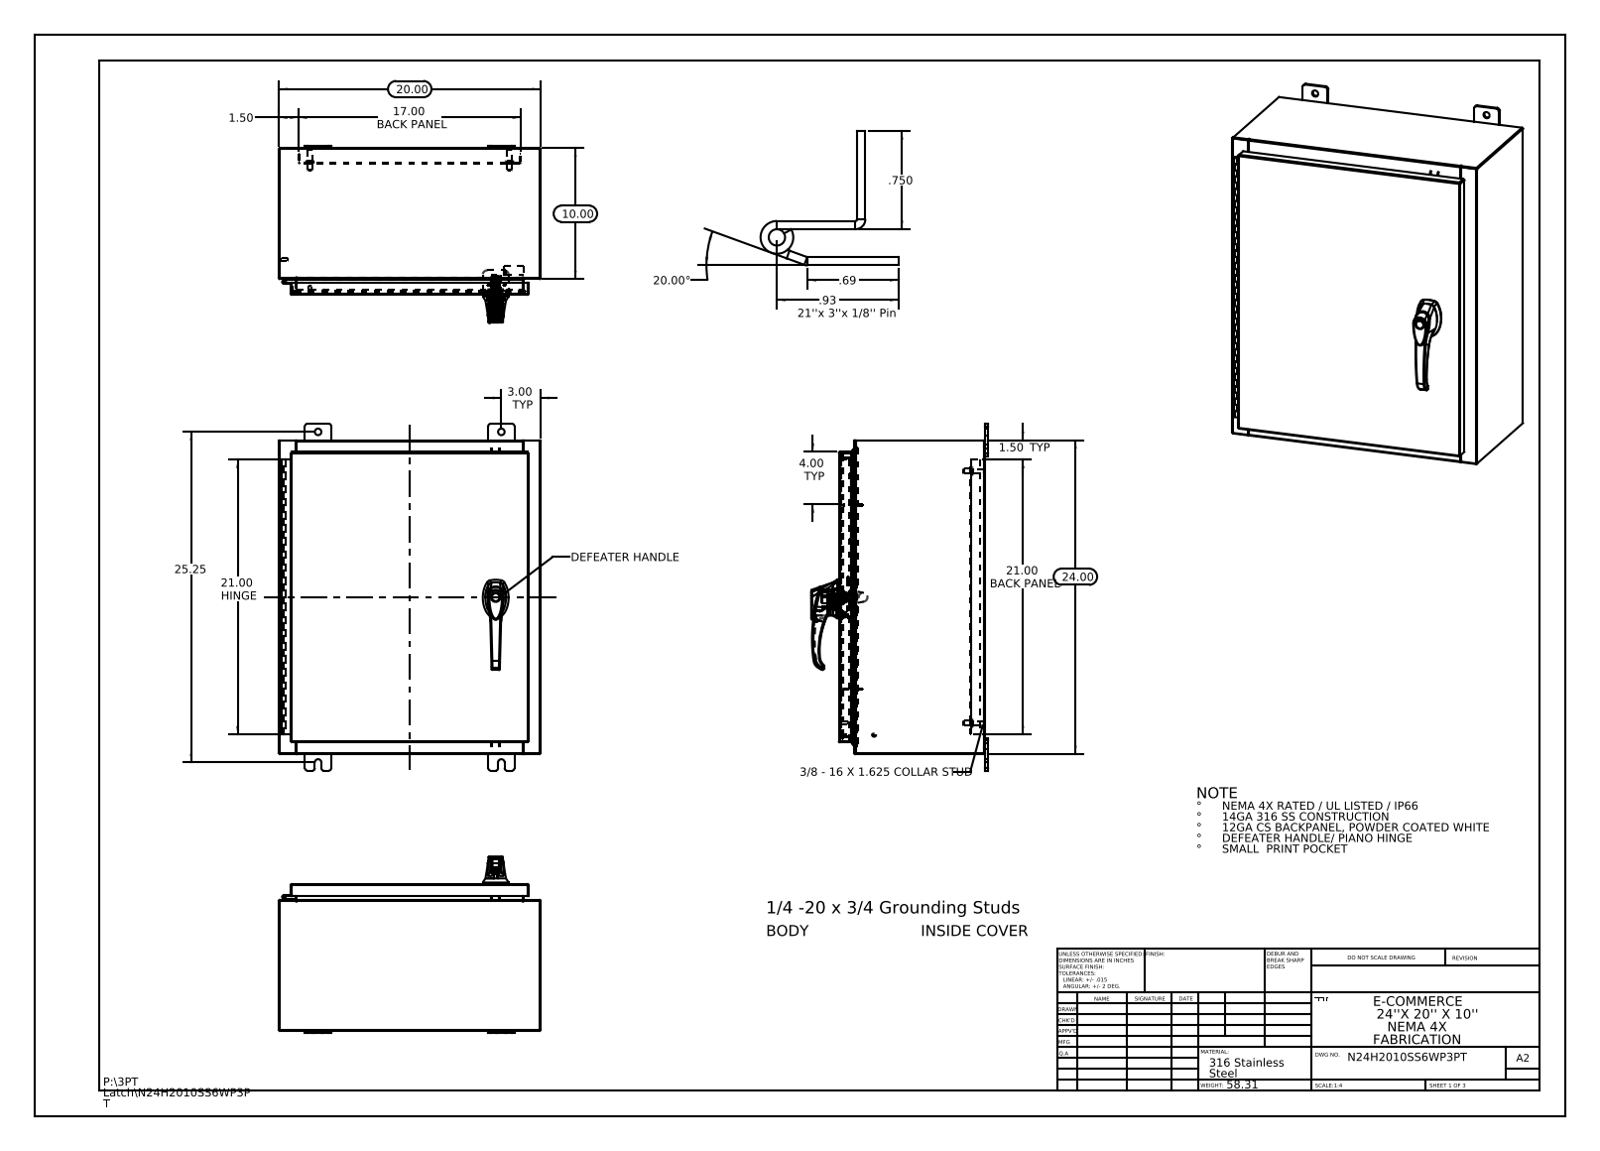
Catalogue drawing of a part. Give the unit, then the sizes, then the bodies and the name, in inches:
Units: inches
Overall size (bounding box): 26.5 × 20 × 13.495
Round holes (diameter × count): ⌀0.5 ×8, ⌀0.25 ×4, ⌀0.138 ×3, ⌀0.161 ×3, ⌀0.079 ×2, ⌀0.203 ×2, ⌀0.313 ×2, ⌀0.437 ×2, ⌀0.125 ×1, ⌀0.125 ×1, ⌀0.197 ×1, ⌀0.276 ×1
Round bosses / shafts (diameter × count): ⌀0.625 ×4, ⌀0.375 ×4, ⌀0.33 ×4, ⌀0.157 ×4, ⌀0.14 ×4, ⌀0.315 ×3, ⌀0.236 ×3, ⌀1.181 ×1
Partial cylindrical surfaces — rounded edges, fillets, slot ends (radius × count): R0.118 ×37, R0.006 ×33, R0.19 ×24, R0.013 ×22, R0.088 ×18, R0.039 ×15, R0.028 ×12, R0.008 ×6
Main face-to-face distances: 0.075, 11.126, 19.925, 11.051, 11.201, 23.925, 0.104, 1, 1.075, 10.051
Hole centre spacings: 7.68, 0.295, 0.625, 0.841, 1.25, 1.313, 1.561, 1.858
Volume: 207.3 in³ · Surface area: 5 156 in²
Bodies: 37 solids, 2498 faces (883 planar, 917 cylindrical, 698 other)
Part name (STEP PRODUCT): 297025; N24H2010SS6WP3PT Cover; 297026; N24H2010SS6WP3PT Defeater Handle - 3 - 2500-51 ZN (+8 more)
STEP written by: SolidWorks 2013 (CONFIG_CONTROL_DESIGN)
